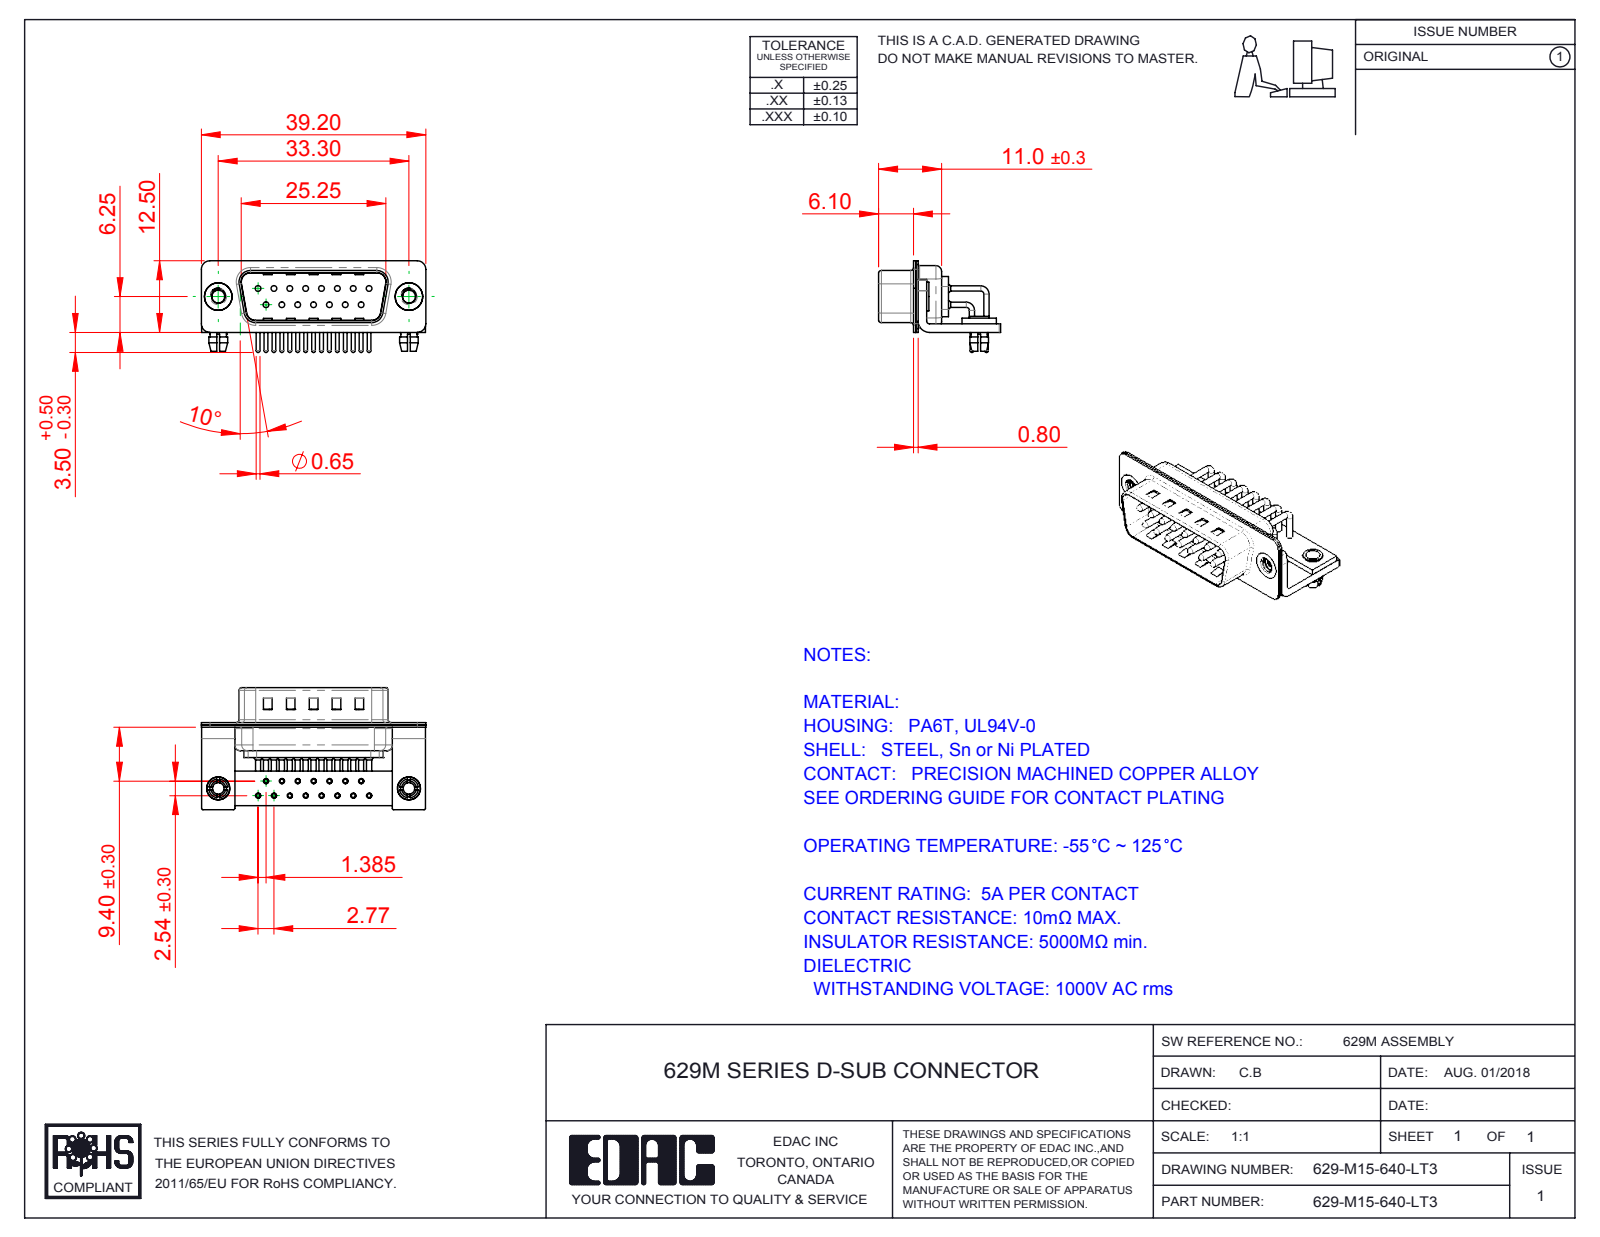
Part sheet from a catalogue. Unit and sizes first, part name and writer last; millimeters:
Units: millimetres
Overall size (bounding box): 39.2 × 21.3 × 16
Round holes (diameter × count): ⌀2 ×17, ⌀0.9 ×15, ⌀1 ×15, ⌀1.7 ×15, ⌀2.26 ×2, ⌀2.5 ×2, ⌀3.2 ×2, ⌀4 ×2, ⌀4.8 ×2
Round bosses / shafts (diameter × count): ⌀0.9 ×21, ⌀1.5 ×15, ⌀0.65 ×15, ⌀5 ×2, ⌀4.9 ×2, ⌀4 ×2, ⌀3.4 ×2, ⌀3.3 ×2
Partial cylindrical surfaces — rounded edges, fillets, slot ends (radius × count): R0.25 ×16, R1.5 ×16, R1.01 ×15, R2 ×13, R0.5 ×9, R1.6 ×8, R0.6 ×4, R0.65 ×4
Main face-to-face distances: 0.4, 1.5, 0.85, 0.8, 1.25, 10.4, 9.55, 1, 1.9, 9.15
Hole centre spacings: 2.77, 5.54, 3.16, 8.31, 4.87, 11.08, 2.89, 7.37
Volume: 2 481 mm³ · Surface area: 6 762 mm²
Bodies: 25 solids, 2162 faces (1173 planar, 757 cylindrical, 232 other)
Part name (STEP PRODUCT): 629M Stabilizer Bracket; 629-M15-640-LT3; 629M Board Lock; 629M Stabilizer Board_15 Contacts (+6 more)
STEP written by: SolidWorks 2016 (CONFIG_CONTROL_DESIGN)
